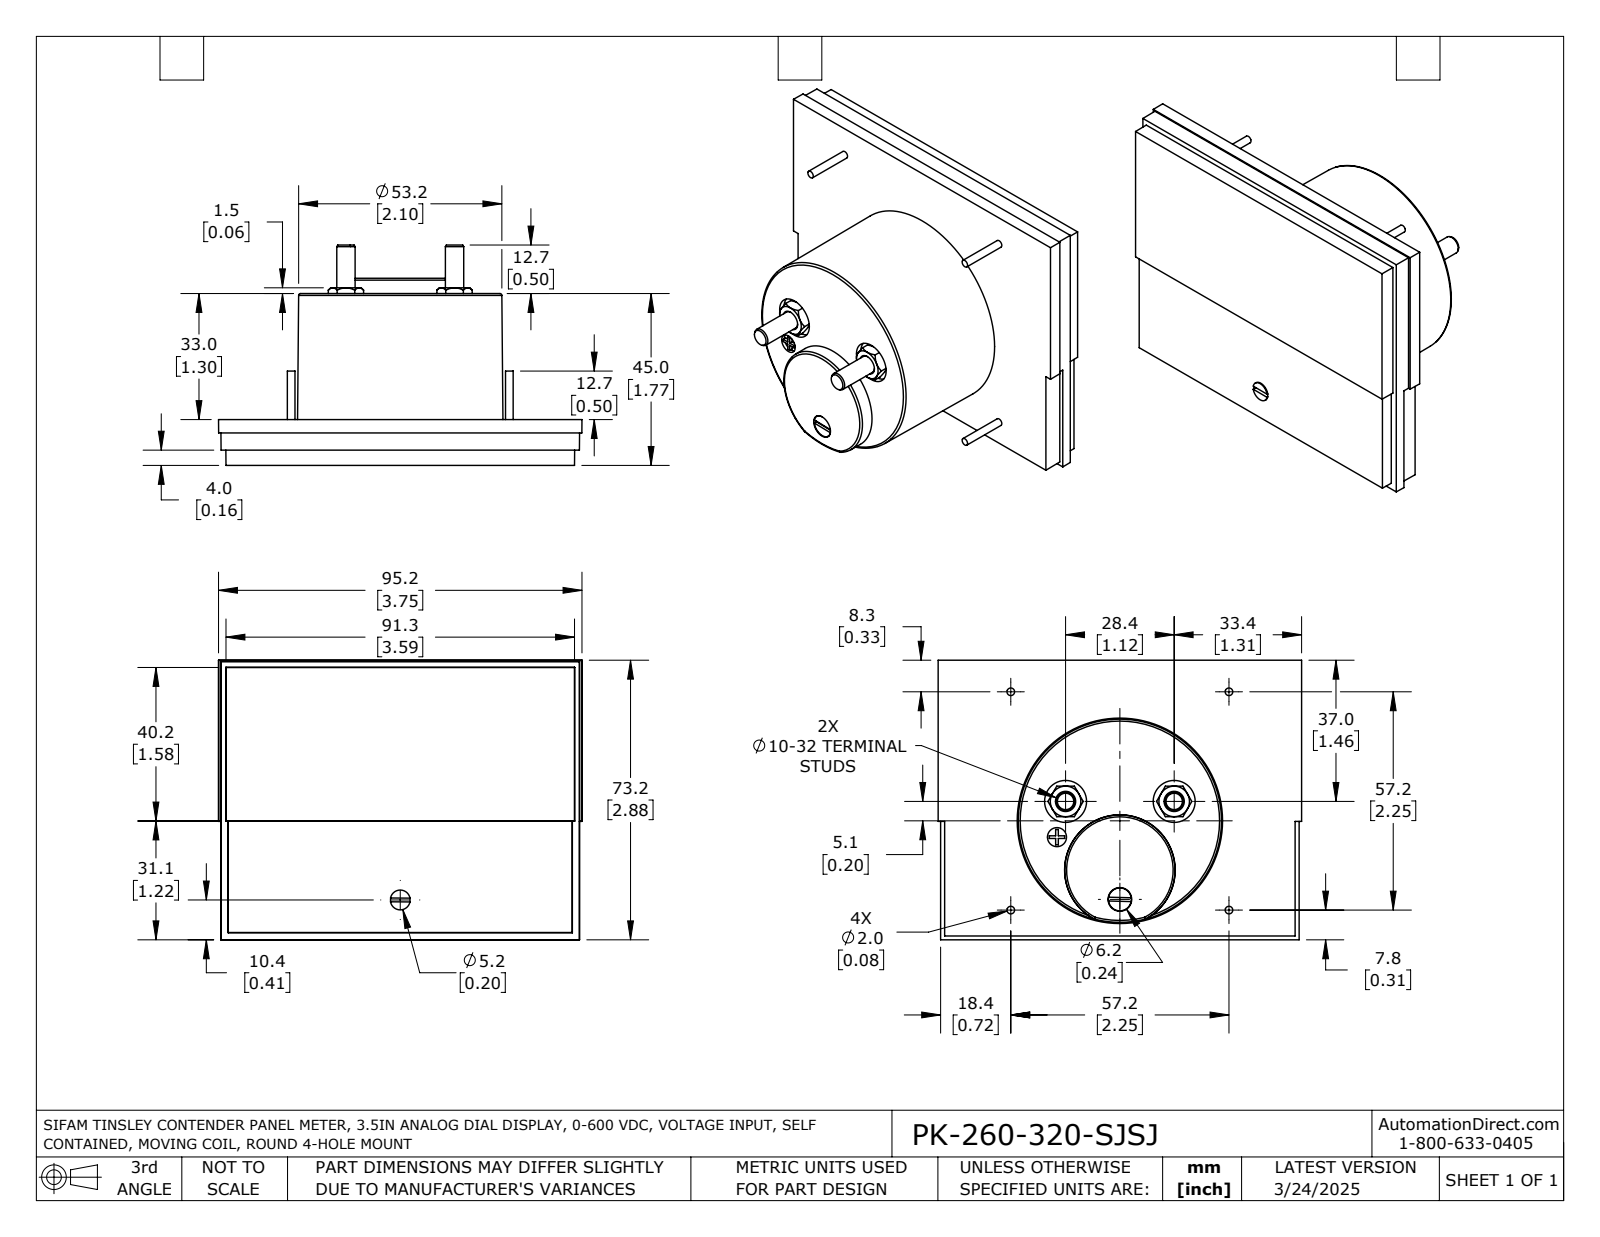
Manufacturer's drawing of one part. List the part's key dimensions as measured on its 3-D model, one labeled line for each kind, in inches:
Part name (STEP PRODUCT): PK-260-320-SJSJ
STEP written by: SolidWorks 2021 (AUTOMOTIVE_DESIGN)
Units: inches
Bodies: 1 solid, 163 faces (76 planar, 31 cylindrical, 56 other)
Overall size (bounding box): 3.748 × 2.882 × 2.272
Volume: 9.446 in³ · Surface area: 38.39 in²
Round holes (diameter × count): ⌀0.433 ×2, ⌀0.197 ×1, ⌀0.244 ×1
Round bosses / shafts (diameter × count): ⌀0.079 ×4, ⌀0.189 ×2, ⌀0.236 ×1, ⌀0.205 ×1
Partial cylindrical surfaces — rounded edges, fillets, slot ends (radius × count): R0.1 ×1
Main face-to-face distances: 0.472, 0.03, 0.443, 1.772, 1.299, 1.742, 0.157, 0.073, 0.315, 1.457
Hole centre spacings: 1.155, 0.379, 0.912, 1.12, 1.263
